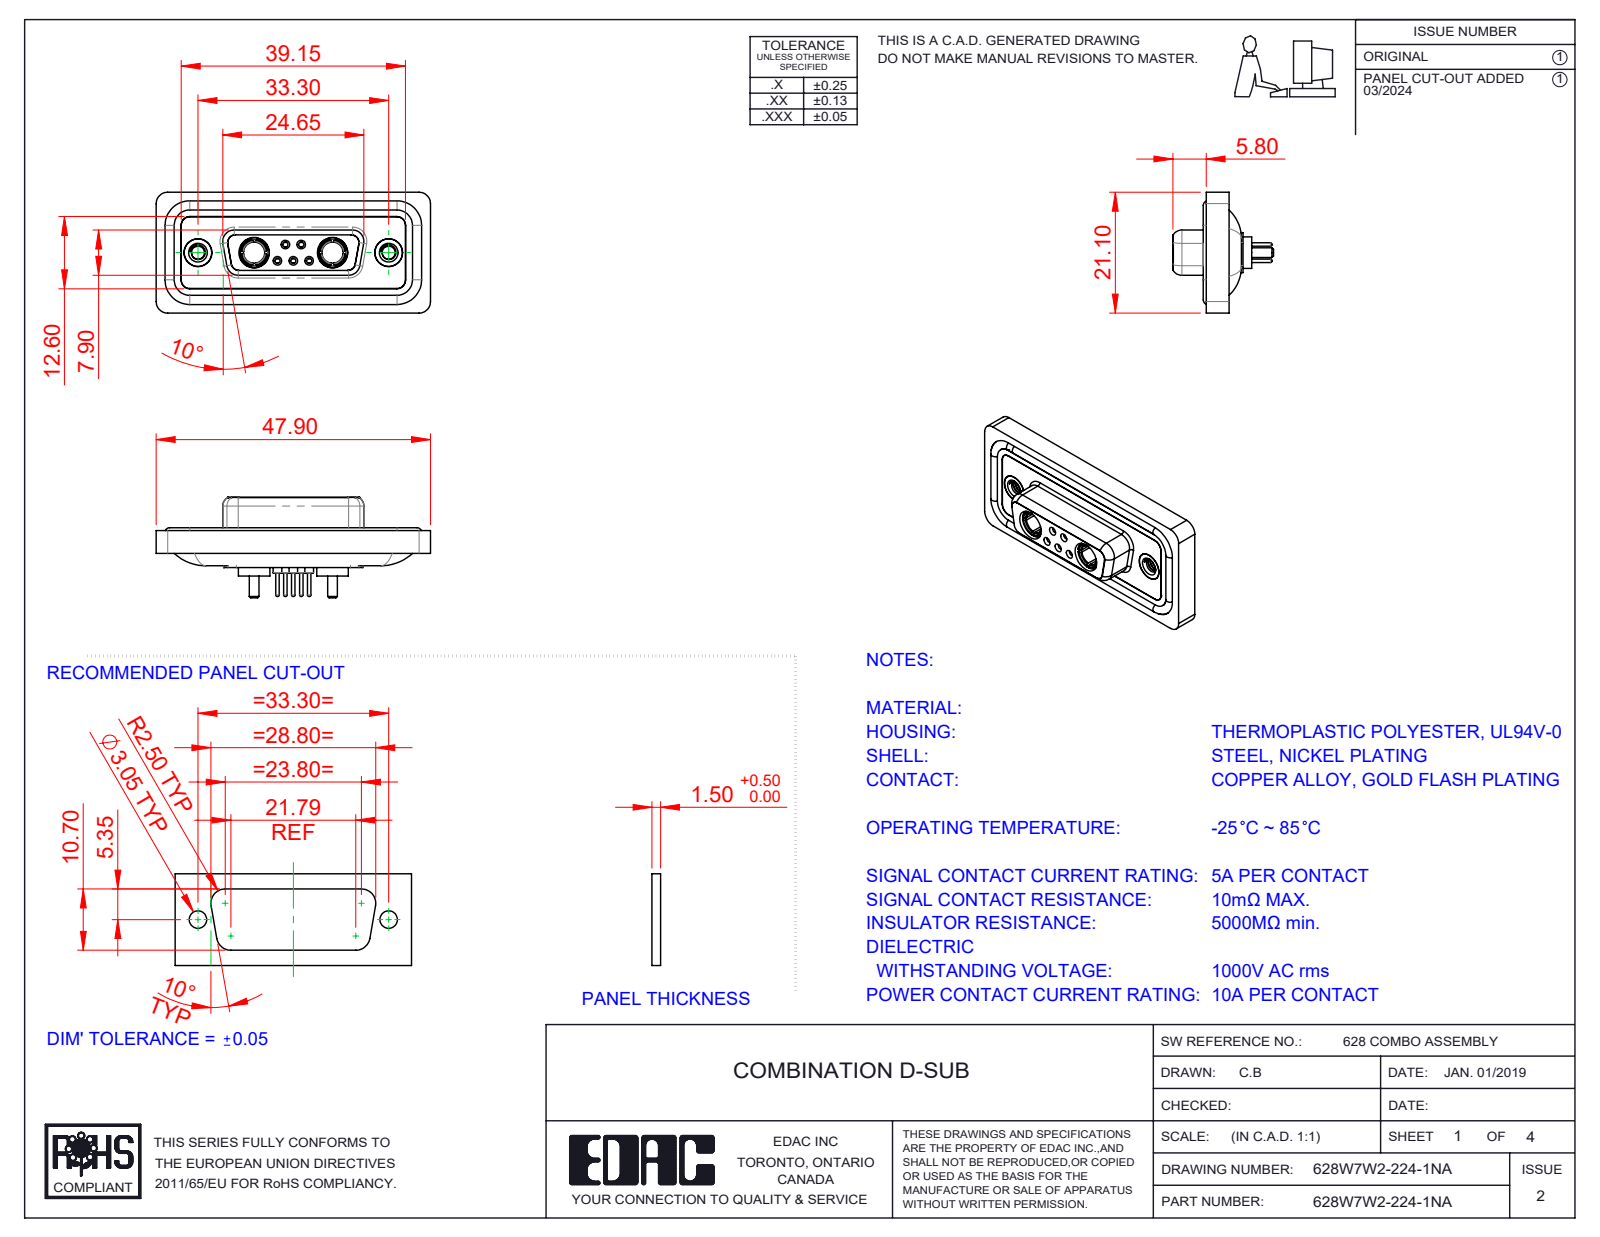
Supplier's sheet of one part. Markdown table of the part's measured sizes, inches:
| quantity | value |
| --- | --- |
| part name | 628Combo Contact Row 1_24; 628Combo Housing_7W2; 628W7W2-224-1NA; 628Combo Contact Row 2_24 (+5 more) |
| STEP written by | SolidWorks 2023 (CONFIG_CONTROL_DESIGN) |
| units | inches |
| bodies | 16 solids, 807 faces (238 planar, 331 cylindrical, 238 other) |
| overall size | 1.886 × 0.831 × 0.691 |
| volume | 0.369 in³ |
| surface area | 15.28 in² |
| round holes (diameter × count) | 0.035 × 5, 0.043 × 5, 0.059 × 5, 0.079 × 5, 0.191 × 4, 0.063 × 3, 0.067 × 2, 0.089 × 2, 0.146 × 2, 0.157 × 2, 0.159 × 2, 0.197 × 2 |
| round bosses / shafts (diameter × count) | 0.063 × 6, 0.087 × 5, 0.024 × 5, 0.217 × 2, 0.205 × 2, 0.195 × 2, 0.195 × 2, 0.189 × 2 |
| partial cylindrical surfaces (radius × count) | 0.059 × 22, 0.079 × 20, 0.053 × 12, 0.063 × 8, 0.01 × 4, 0.02 × 4, 0.024 × 4, 0.026 × 4 |
| main face-to-face distances | 0.016, 0.071, 0.063, 0.02, 0.114, 0.043, 0.293, 0.222, 0.26, 0.278 |
| hole center spacings | 0.124, 0.109, 0.386, 0.925, 0.17, 0.17, 0.198, 0.198 |
